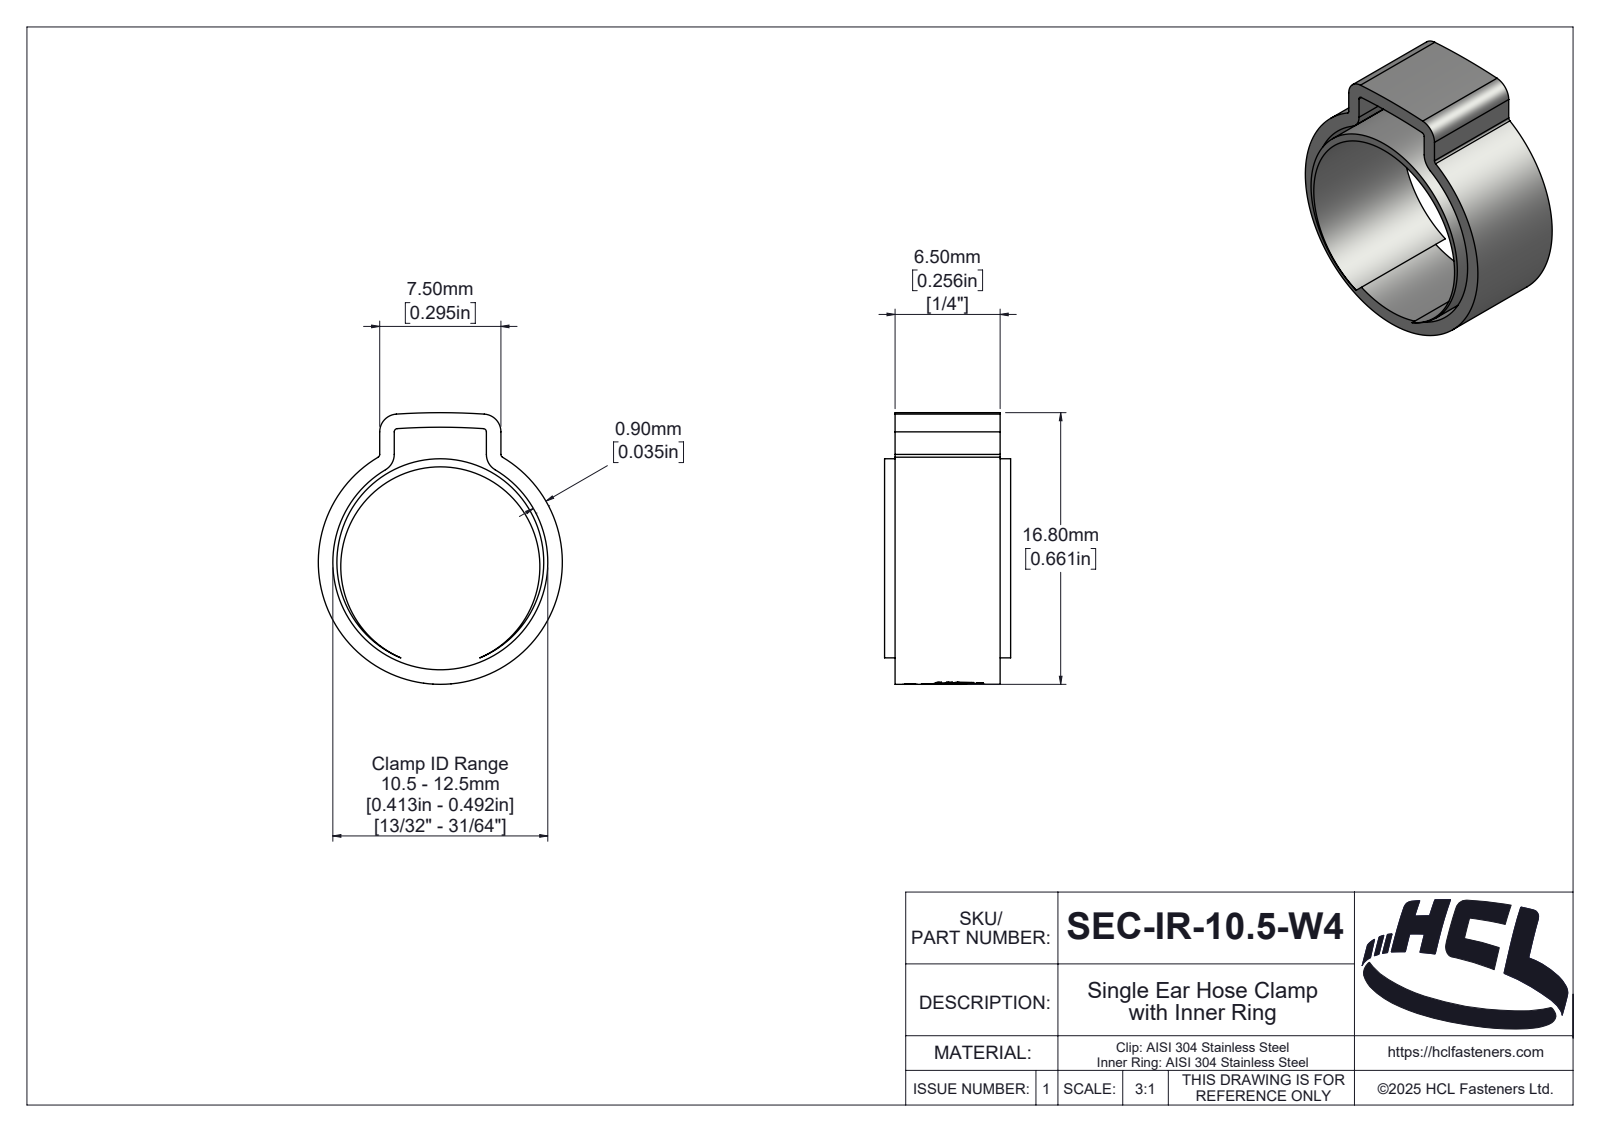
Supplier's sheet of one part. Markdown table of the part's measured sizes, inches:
| quantity | value |
| --- | --- |
| part name | SEC-IR-10.5-W4 |
| STEP written by | SolidWorks 2025 (AUTOMOTIVE_DESIGN) |
| units | inches |
| bodies | 2 solids, 131 faces (10 planar, 72 cylindrical, 49 other) |
| overall size | 0.661 × 0.594 × 0.307 |
| volume | 0.022 in³ |
| surface area | 1.981 in² |
| round holes (diameter × count) | 0.485 × 1, 0.524 × 1 |
| round bosses / shafts (diameter × count) | 0.594 × 1, 0.504 × 1 |
| partial cylindrical surfaces (radius × count) | 0.008 × 4, 0.043 × 4, 0.008 × 1, 0.035 × 1, 0.043 × 1, 0.045 × 1, 0.055 × 1, 0.078 × 1 |
| main face-to-face distances | 0.256, 0.026, 0.281, 0.035, 0.26, 0.307, 0.295, 0.224, 0.136, 0.101 |
